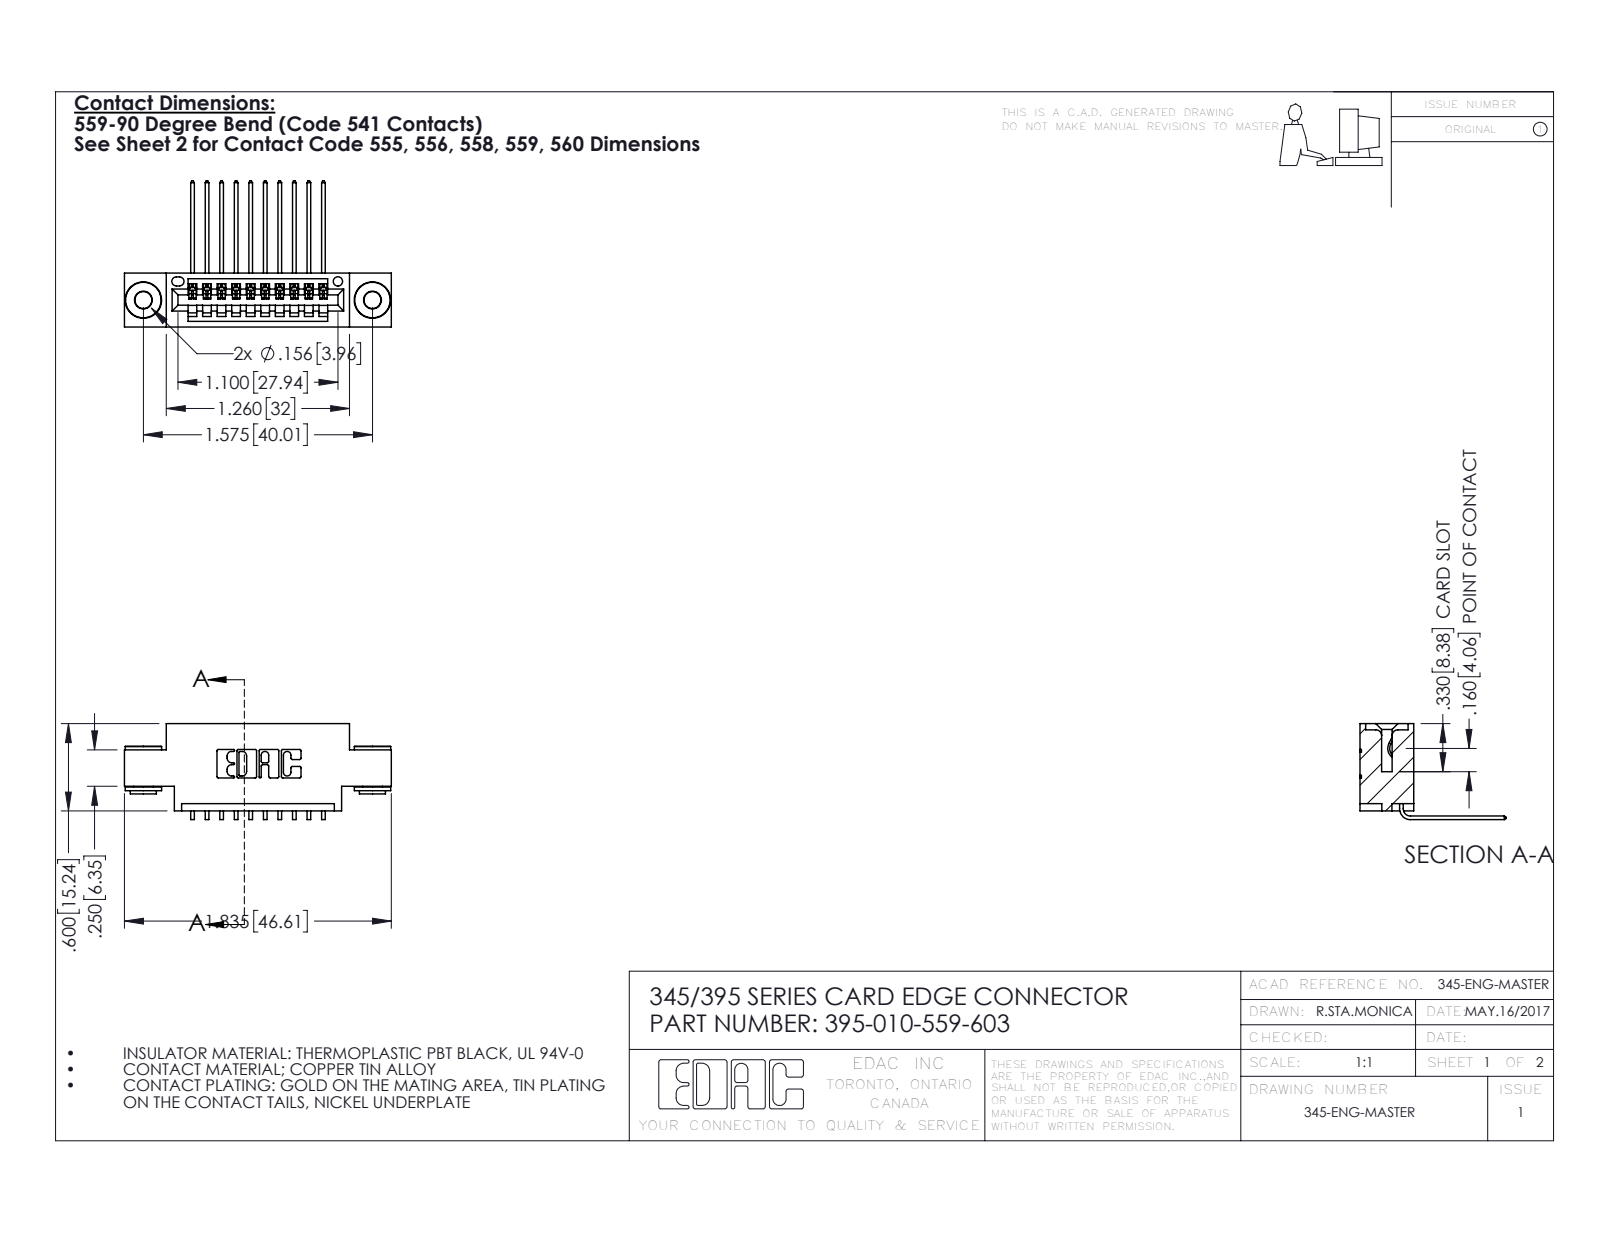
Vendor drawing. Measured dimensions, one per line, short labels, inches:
name: 345 Part_0.170 Offset - 0.156 Dia-TH; 345-250-002_345-250-002-102; 395-010-559-603; 345-292-001_558 559 Tail - 1
written by: SolidWorks 2016 (CONFIG_CONTROL_DESIGN)
unit: in
bodies: 13 solids, 768 faces (514 planar, 246 cylindrical, 8 other)
size: 1.835 × 1.005 × 0.659
volume: 0.25 in³; area: 8.612 in²
holes: 2× ⌀0.116, 2× ⌀0.156, 1× ⌀0.064
bosses: 2× ⌀0.25, 2× ⌀0.18, 2× ⌀0.136
rounds: 22× R0.01, 20× R0.006, 6× R0.007, 6× R0.031, 3× R0.026, 2× R0.031, 2× R0.04, 1× R0.014
face distances: 0.37, 0.072, 0.298, 0.2, 0.1, 0.098, 0.272, 0.025, 0.6, 0.175
hole spacings: 0.27, 1.344, 1.575
